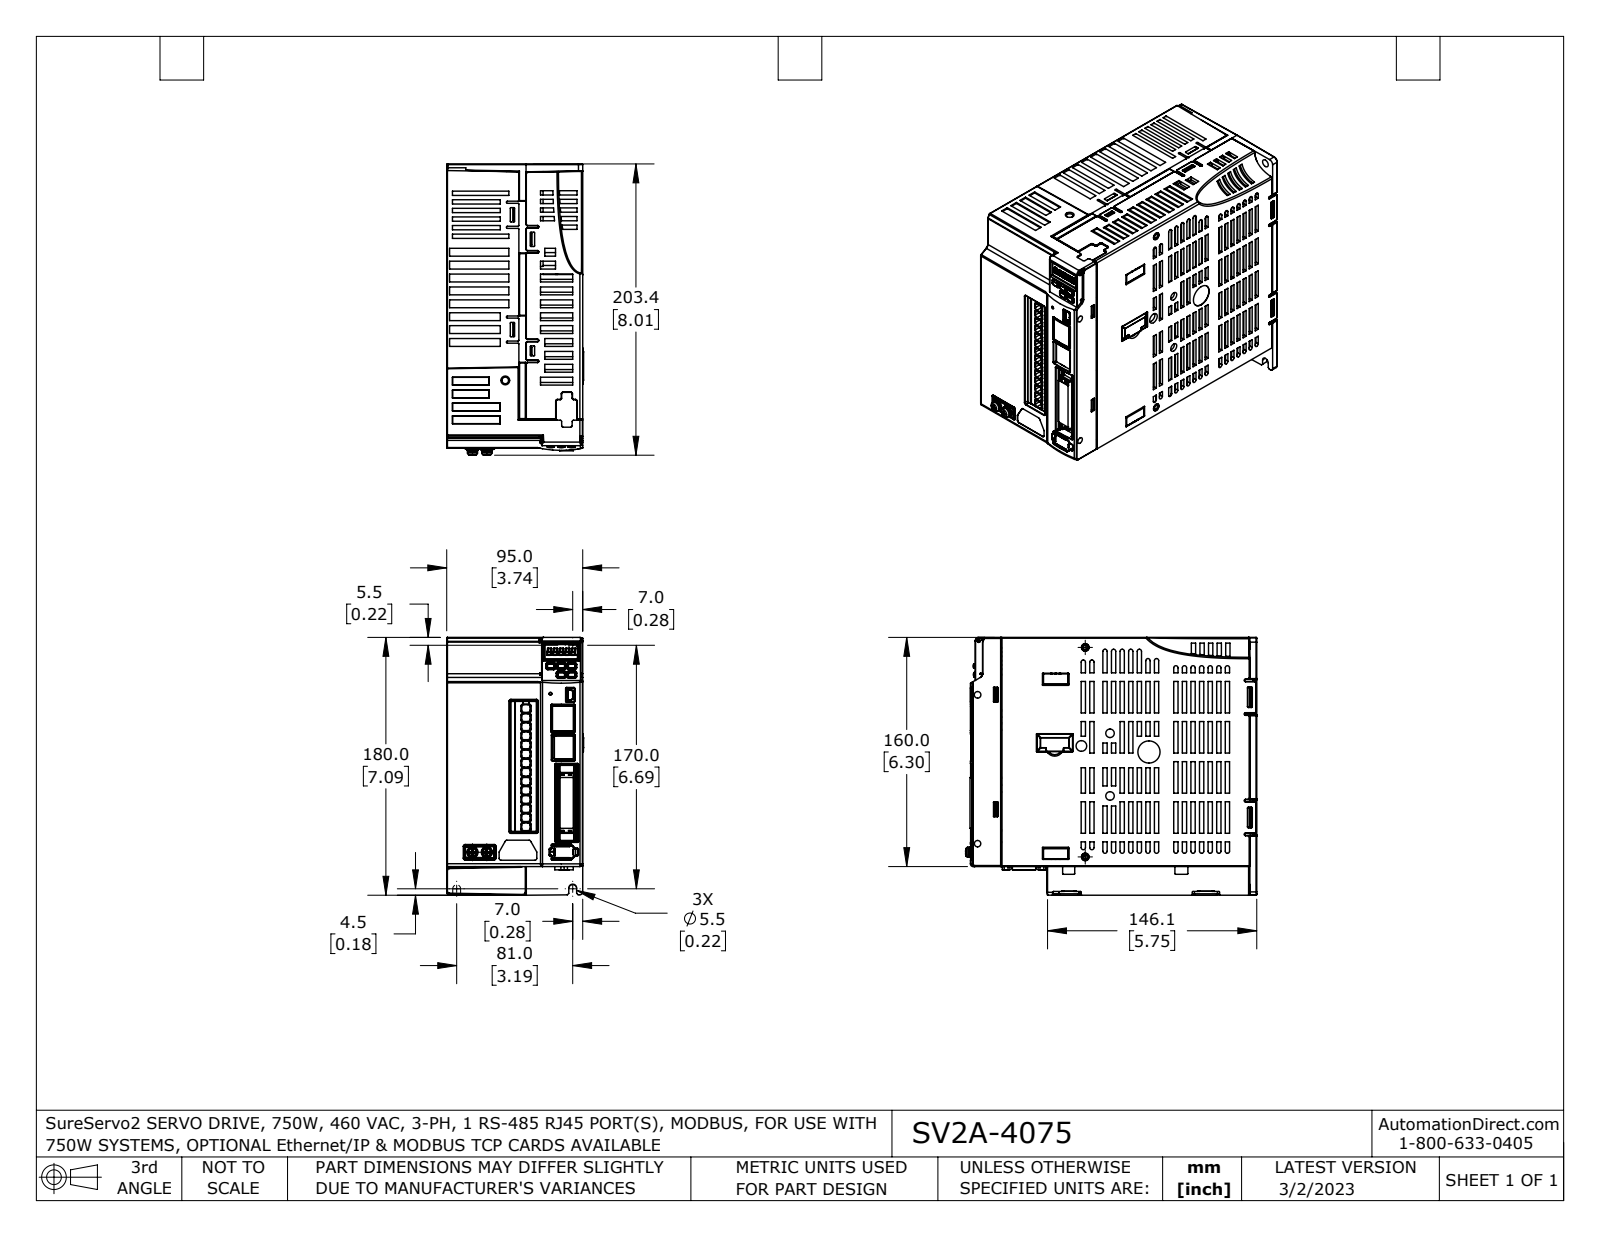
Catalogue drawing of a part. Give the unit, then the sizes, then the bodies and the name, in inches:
Units: inches
Overall size (bounding box): 8.206 × 7.087 × 3.78
Round holes (diameter × count): ⌀0.044 ×15, ⌀0.177 ×4, ⌀0.067 ×2, ⌀0.087 ×2, ⌀0.213 ×1, ⌀0.217 ×1, ⌀1.203 ×1, ⌀1.913 ×1
Round bosses / shafts (diameter × count): ⌀0.307 ×2, ⌀0.276 ×2, ⌀0.256 ×2, ⌀0.157 ×2, ⌀1.317 ×1, ⌀0.687 ×1, ⌀0.378 ×1
Partial cylindrical surfaces — rounded edges, fillets, slot ends (radius × count): R0.02 ×440, R0.059 ×131, R0.039 ×89, R0.012 ×71, R0.004 ×37, R0.108 ×30, R0.008 ×22, R0.098 ×11
Main face-to-face distances: 0.059, 3.74, 0.047, 3.681, 3.681, 0.059, 3.693, 0.047, 0.06, 3.633
Hole centre spacings: 0.09, 0.09, 0.156, 0.238, 0.18, 0.18, 0.239, 0.27
Volume: 42.69 in³ · Surface area: 462.9 in²
Bodies: 7 solids, 4098 faces (2159 planar, 1256 cylindrical, 683 other)
Part name (STEP PRODUCT): SV2A-4040_4075_4150 w sketches 1a wsplts 1a red BbDCc coord fxt sr1
STEP written by: SolidWorks 2021 (AUTOMOTIVE_DESIGN)
